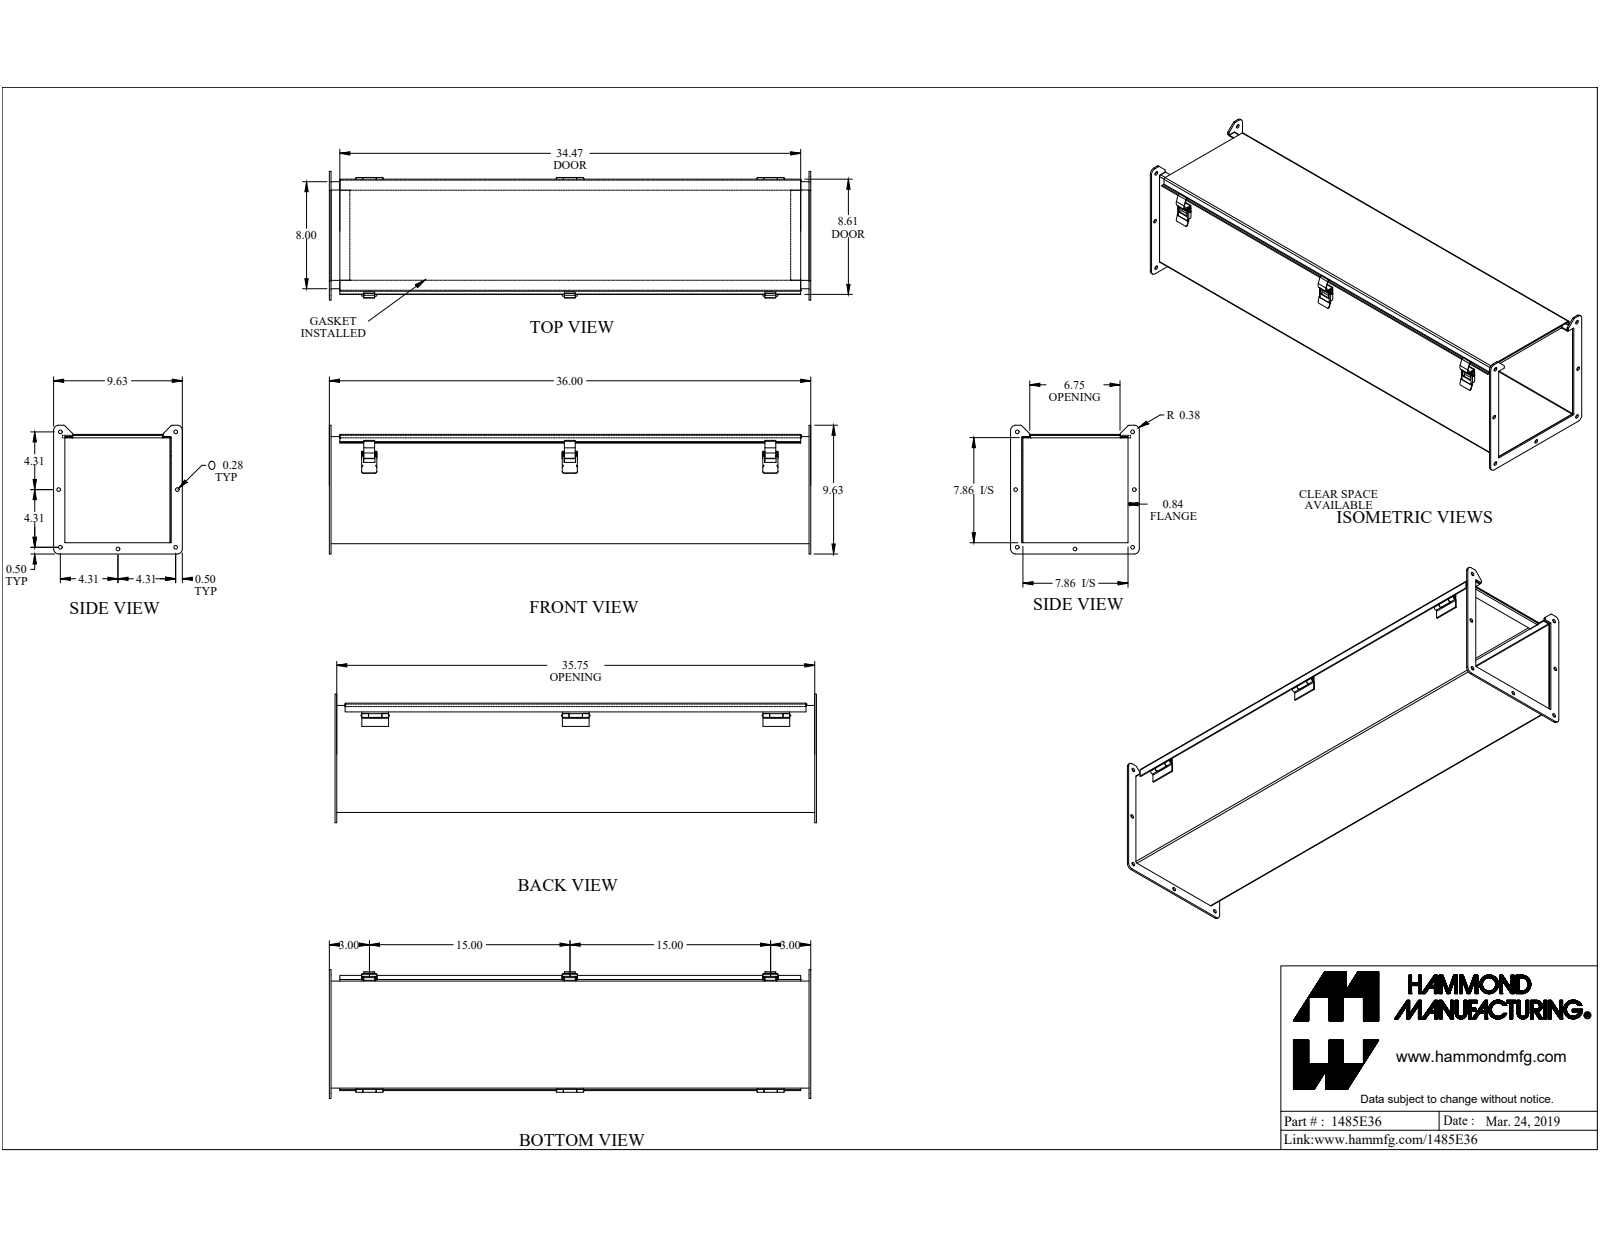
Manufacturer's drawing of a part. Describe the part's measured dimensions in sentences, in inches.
The part is named "1485E36". Its 3-D file was written by "SolidWorks 2019 (CONFIG_CONTROL_DESIGN)". It is 26 solids with 561 faces: 334 planar, 221 cylindrical and 6 other. Overall it measures 36 by 9.625 by 9.625 inches. Its volume is 107 cubic inches and its surface area 2 782 square inches. Round holes: 7 of diameter 0.281, 1 of diameter 0.125, 1 of diameter 0.13, 1 of diameter 0.164. Round bosses or shafts: 2 of diameter 0.187, 1 of diameter 0.275, 1 of diameter 0.156, 1 of diameter 0.125, 1 of diameter 0.125. Partial cylindrical surfaces (rounded edges, fillets, slot ends): 19 of radius 0.016, 11 of radius 0.125, 7 of radius 0.035, 7 of radius 0.036, 7 of radius 0.039, 7 of radius 0.076, 7 of radius 0.108, 6 of radius 0.015. The main face-to-face distances are 0.072, 7.928, 8.1, 8, 7.856, 8.028, 8.172, 0.172, 7.913, 7.841. The hole center spacings are 8.625, 4.314, 4.315, 9.755, 9.755, 6.276, 12.197, 0.285.
